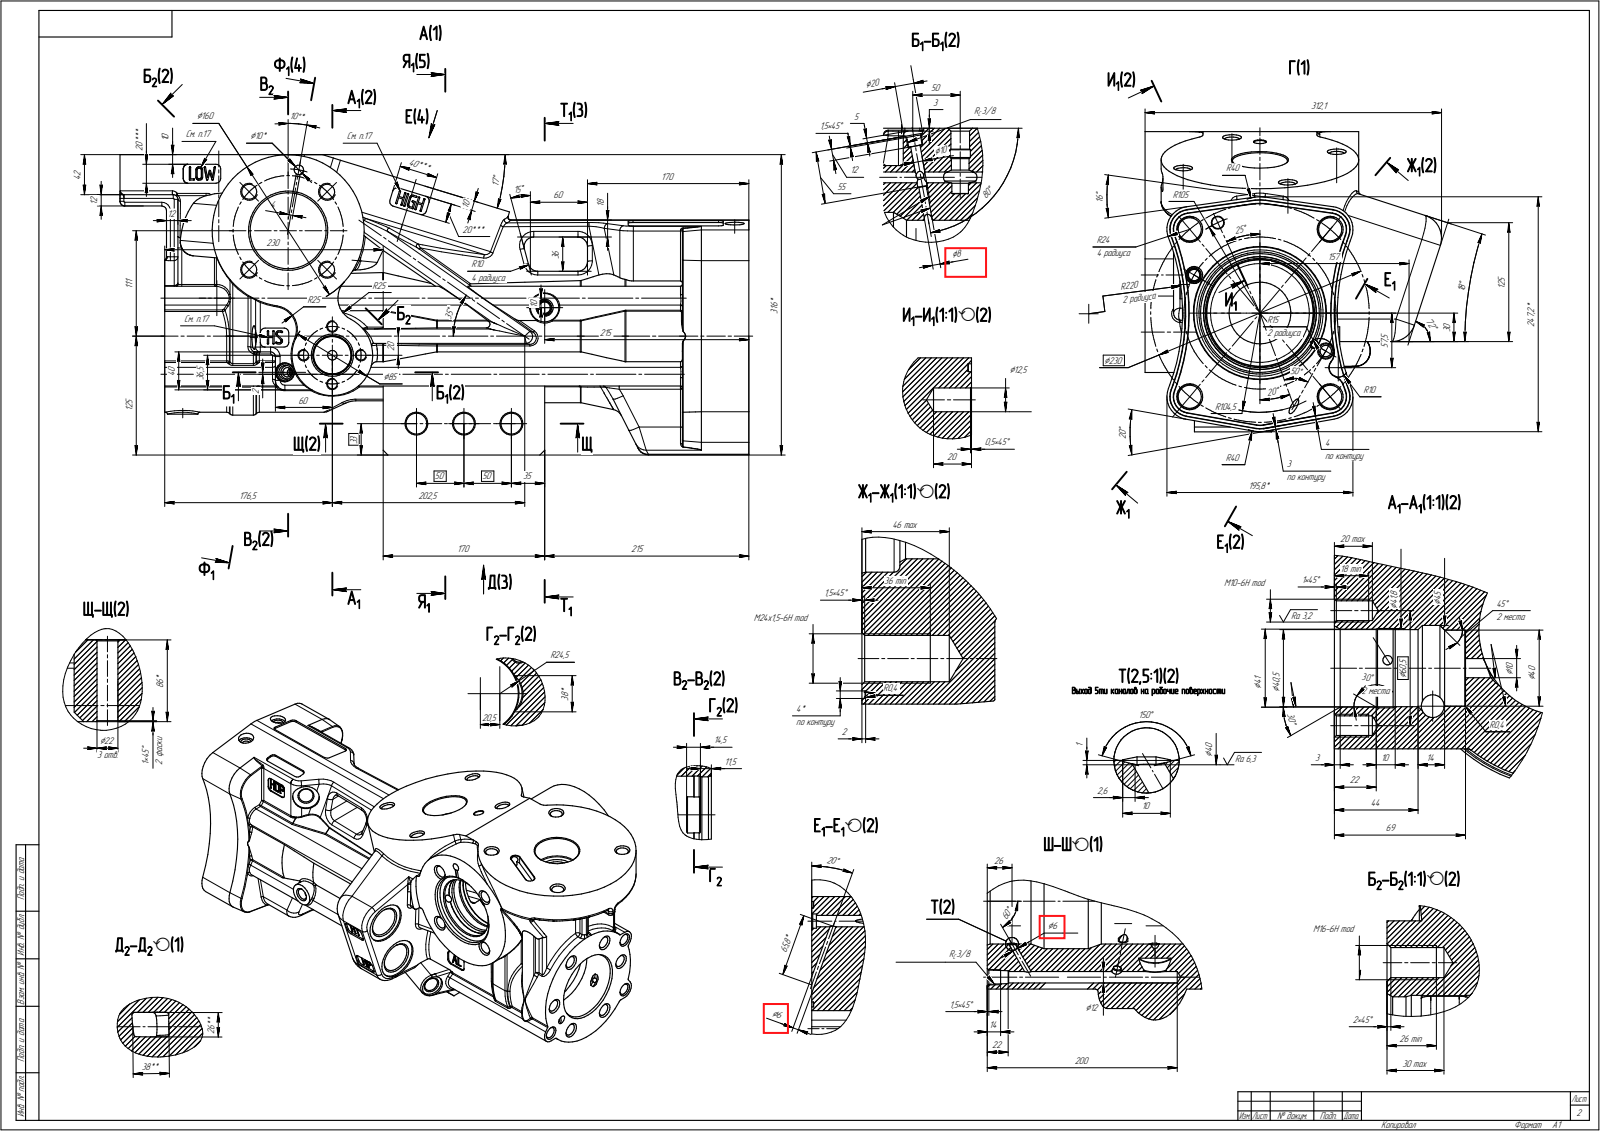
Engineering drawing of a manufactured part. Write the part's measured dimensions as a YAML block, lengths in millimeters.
part_name: "\\X2\\041A043E0440043F04430441\\X0\\"
step_written_by: "Autodesk Inventor 2014 (AUTOMOTIVE_DESIGN)"
units: millimeters
bodies: {solids: 1, faces: 171, planar: 28, cylindrical: 57, other: 86}
overall_size: [1317.33, 126.49, 60]
volume: 2170000
surface_area: 304933
round_holes:
  - {diameter: 12, count: 3}
  - {diameter: 9, count: 2}
  - {diameter: 3.24, count: 1}
  - {diameter: 4.92, count: 1}
  - {diameter: 6.4, count: 1}
partial_cylinders:
  - {radius: 10, count: 8}
  - {radius: 5, count: 6}
  - {radius: 3, count: 4}
  - {radius: 4.5, count: 4}
  - {radius: 9.5, count: 4}
  - {radius: 20, count: 2}
  - {radius: 10.5, count: 1}
  - {radius: 19.5, count: 1}
face_to_face_distances: [16, 11, 19, 38, 22, 27, 8, 30, 3, 41]
hole_center_spacings: [521.59, 30, 1040]
